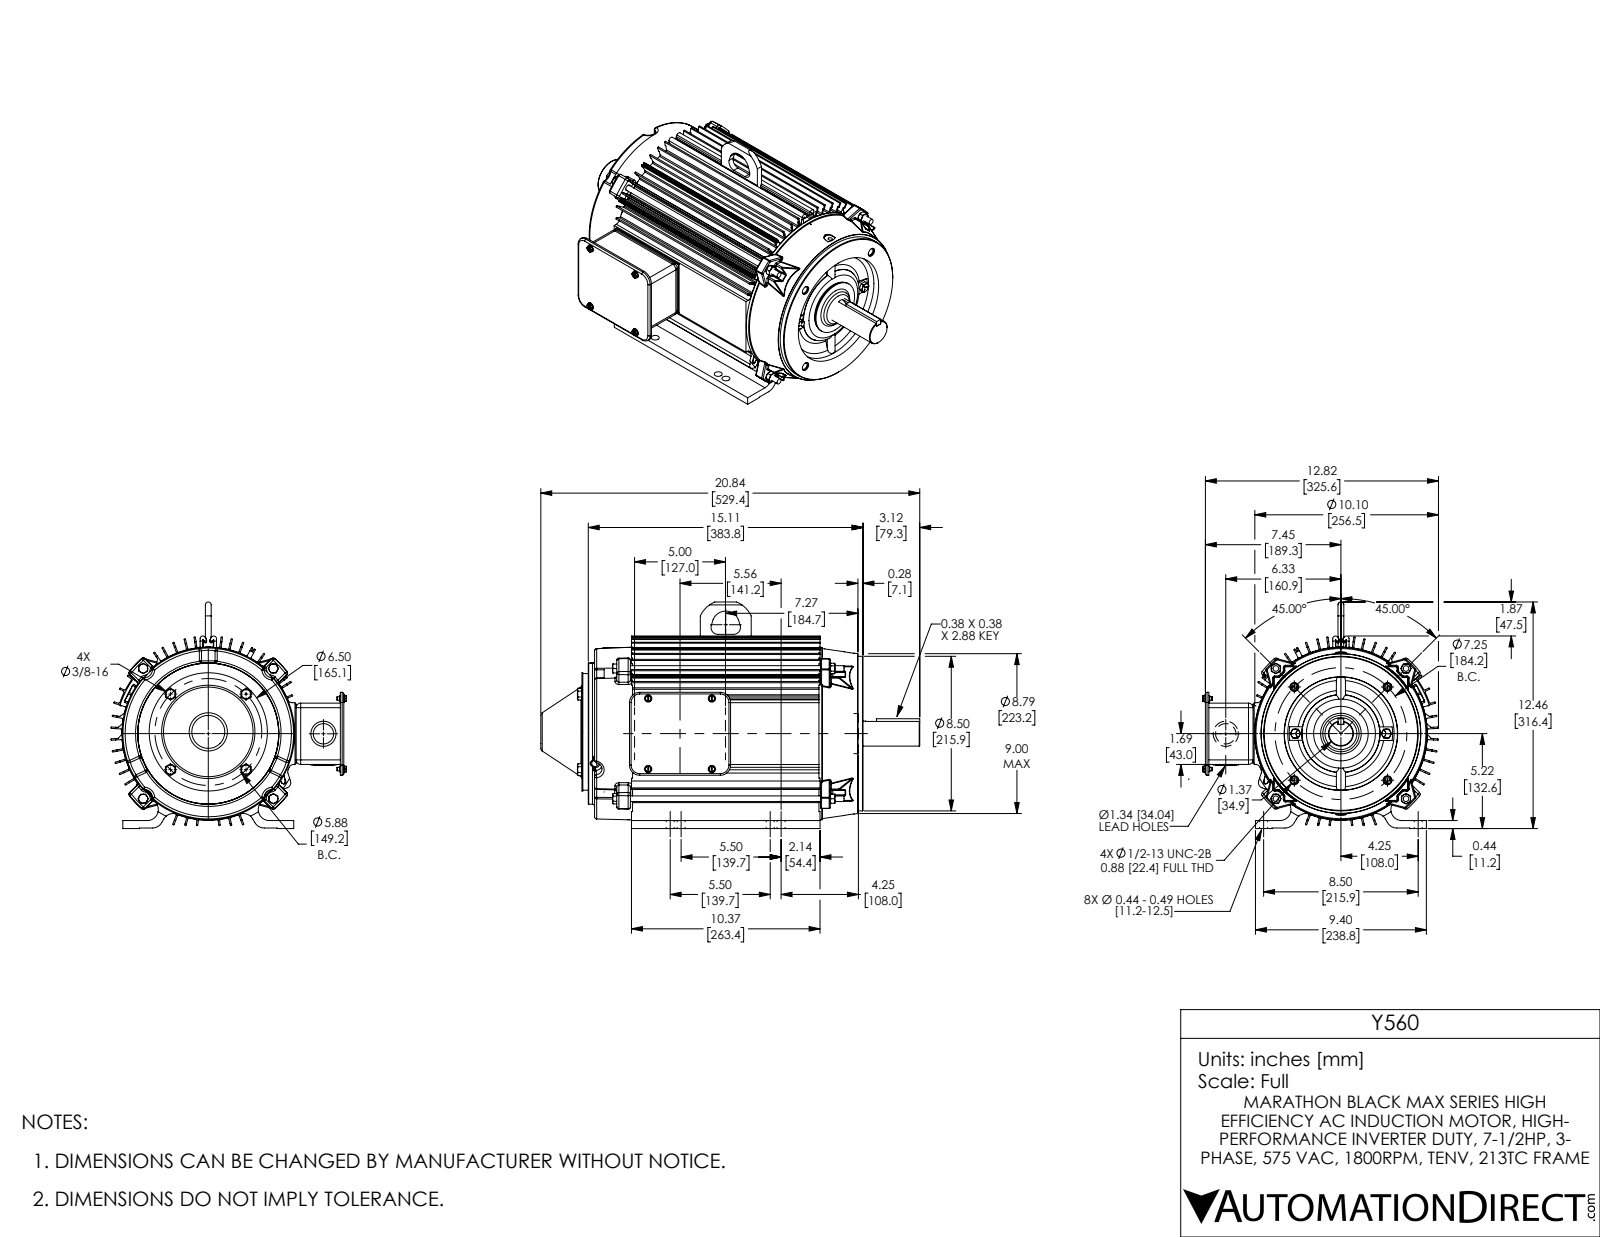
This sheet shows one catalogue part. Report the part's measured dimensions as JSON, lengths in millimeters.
{"part_name": "SS330105-1025_RevA.S r1a Ext1 C R1C motor WITH Rear Cover 1", "step_written_by": "SolidWorks 2017 (AUTOMOTIVE_DESIGN)", "units": "millimeters", "bodies": {"solids": 28, "faces": 3679, "planar": 995, "cylindrical": 1028, "other": 1656}, "overall_size": [521.8, 329.1, 316.4], "volume_mm3": 6407000, "surface_area_mm2": 1688000, "round_holes": [[11.1, 8], [8.7, 6], [4.4, 4], [4.4, 4], [5.6, 4], [6.5, 4], [7.9, 4], [7.9, 4], [10.3, 4], [10.7, 4], [6.4, 2], [8.4, 2]], "round_bosses_or_shafts": [[7.9, 6], [12.7, 4], [10.1, 4], [9.5, 4], [7.5, 4], [4.8, 4], [11.2, 2], [235.5, 1]], "partial_cylinders_radius": [[1.5, 162], [3, 130], [1, 32], [6.4, 25], [0.8, 19], [4.8, 12], [2.4, 8], [6.4, 8]], "face_to_face_distances": [1.9, 61.9, 1.5, 66.6, 2.5, 69.4, 321.9, 383.8, 68.1, 65], "hole_center_spacings": [118.5, 148.7, 158.2, 53.8, 101.6, 15.2, 17.5, 36.5]}
